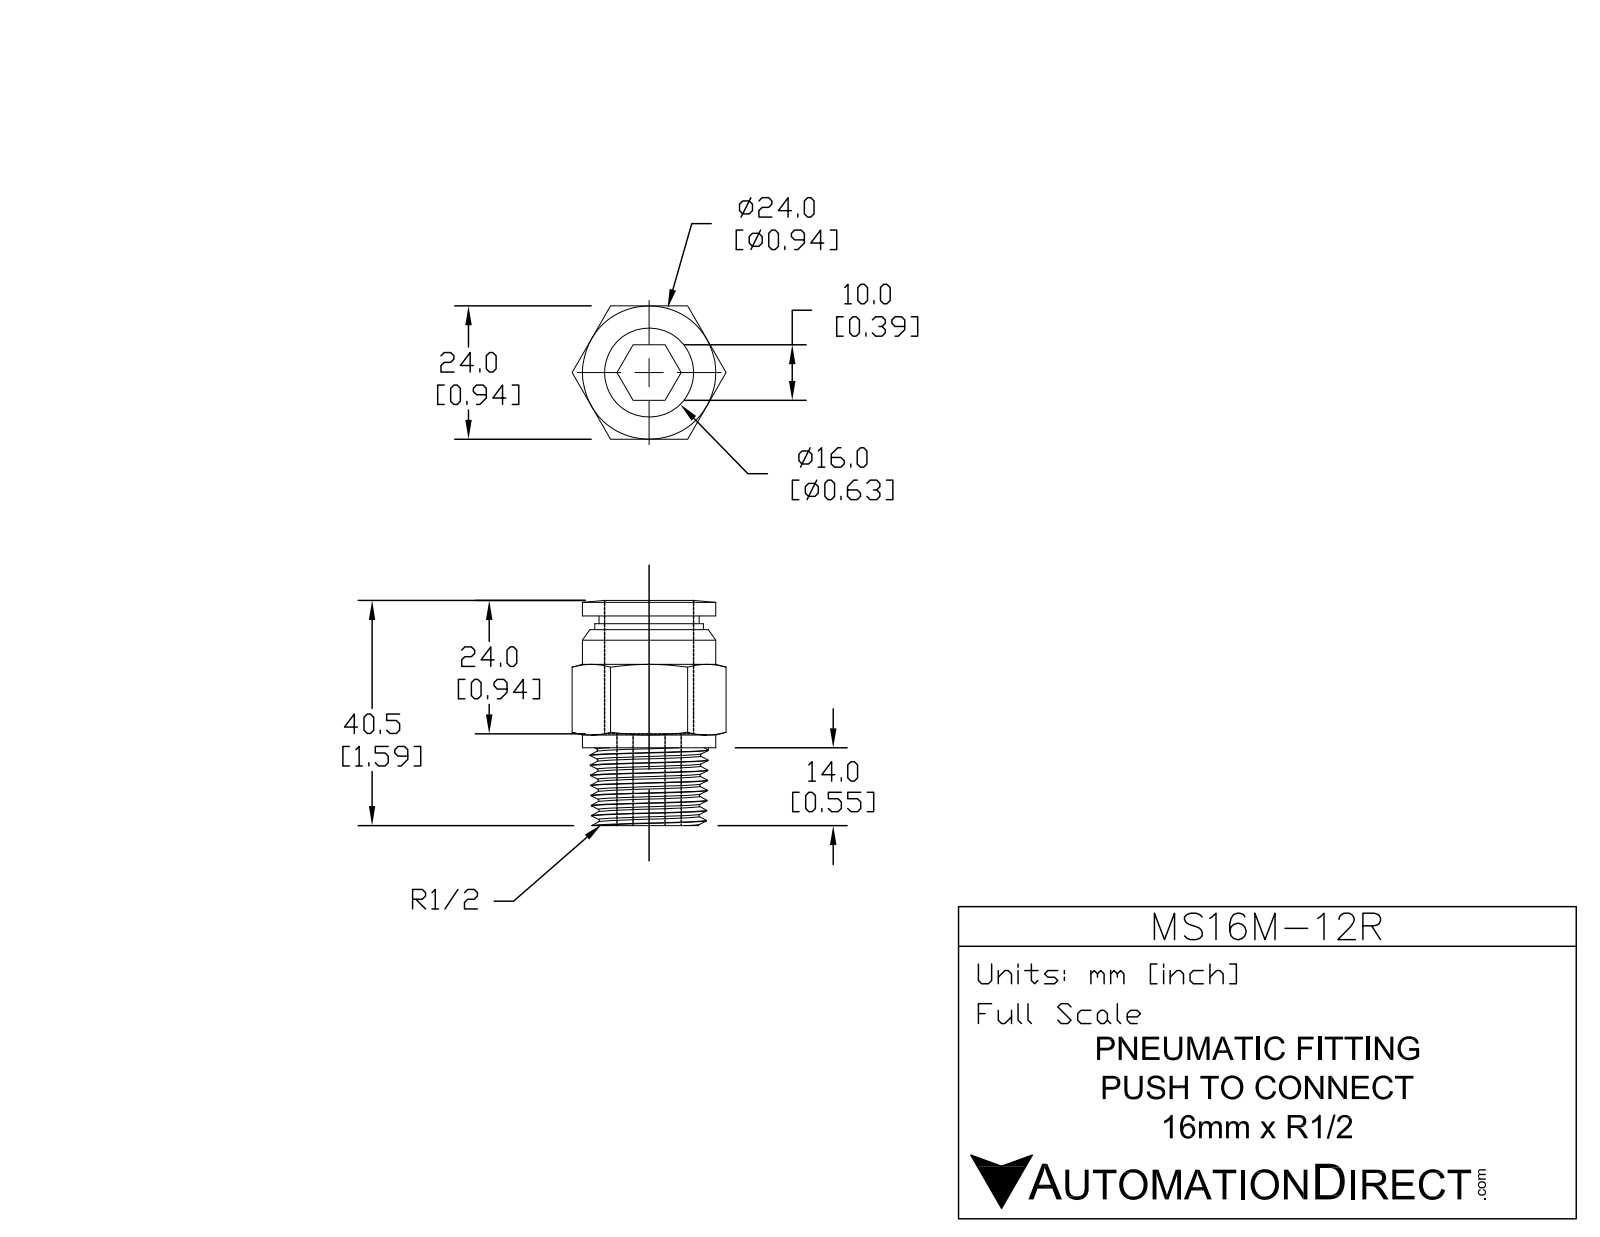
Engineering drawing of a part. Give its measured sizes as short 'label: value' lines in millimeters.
name: MS16M-12R
written by: SolidWorks 2015 (AUTOMOTIVE_DESIGN)
unit: mm
bodies: 1 solid, 53 faces (13 planar, 14 cylindrical, 26 other)
size: 40.5 × 27.7 × 25.2
volume: 10 300 mm³; area: 5 814 mm²
holes: 1× ⌀10, 1× ⌀16.3
bosses: 1× ⌀25.2, 1× ⌀24, 1× ⌀22, 1× ⌀20.2, 1× ⌀18
face distances: 24, 21.2, 16.5, 37.7, 35.7, 19.2, 2, 36.1, 19.6, 0.4
